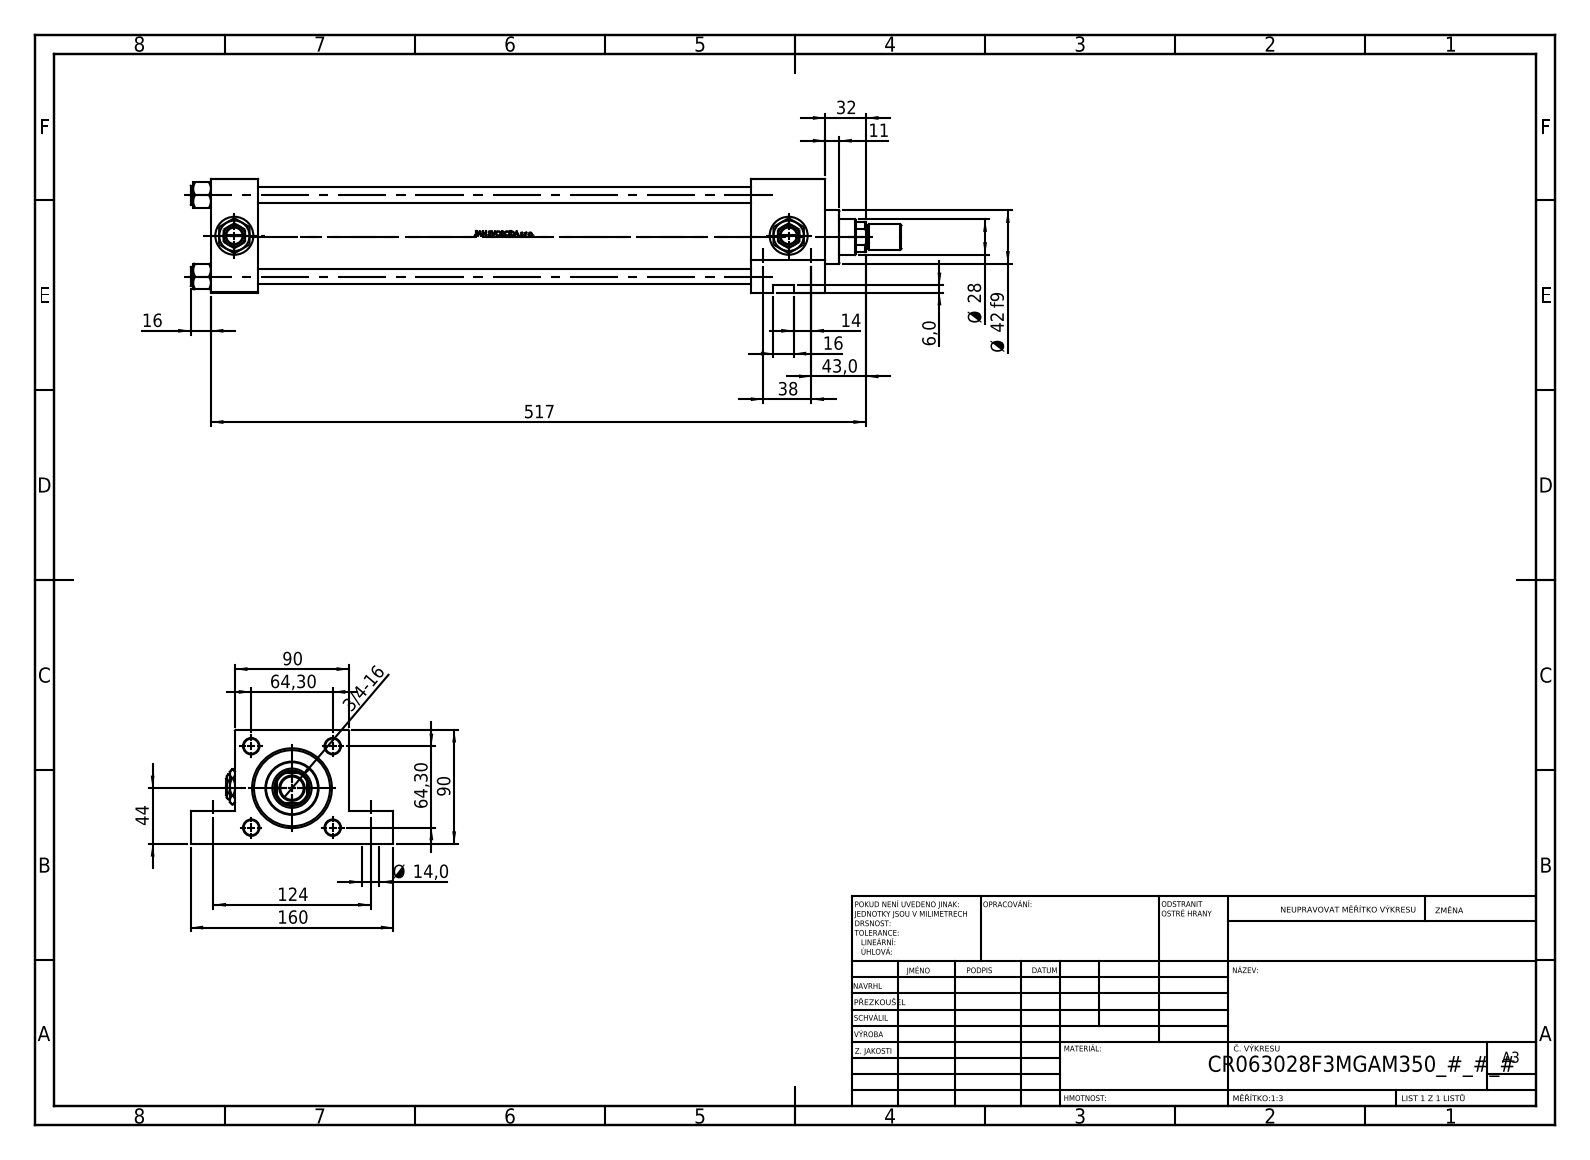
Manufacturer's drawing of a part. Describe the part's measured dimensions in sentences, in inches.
The part is named "NUT_M5_F; V215CR_F_Body; V215CR_VCP_F; Zatka_pro_OIL_PORT (+3 more)". Its 3-D file was written by "SolidWorks 2019 (CONFIG_CONTROL_DESIGN)". It is 14 solids with 1217 faces: 489 planar, 140 cylindrical and 588 other. Overall it measures 22.087 by 6.299 by 3.543 inches. Its volume is 96.97 cubic inches and its surface area 646.1 square inches. Round holes: 4 of diameter 0.472, 4 of diameter 0.551, 4 of diameter 0.825, 4 of diameter 1.181, 3 of diameter 0.276, 1 of diameter 0.728, 1 of diameter 1.102, 1 of diameter 1.22, 1 of diameter 1.969, 1 of diameter 2.362, 1 of diameter 2.48. Round bosses or shafts: 4 of diameter 0.591, 1 of diameter 2.717, 1 of diameter 1.654, 1 of diameter 0.787, 1 of diameter 0.709. Partial cylindrical surfaces (rounded edges, fillets, slot ends): 1 of radius 0.531. The main face-to-face distances are 3.543, 1.457, 19.094, 17.638, 16.772, 15.315, 2.323, 1.024, 2.52, 17.965. The hole center spacings are 2.531, 1.496, 1.763, 1.818, 2.472, 2.678, 3.58, 4.882.
